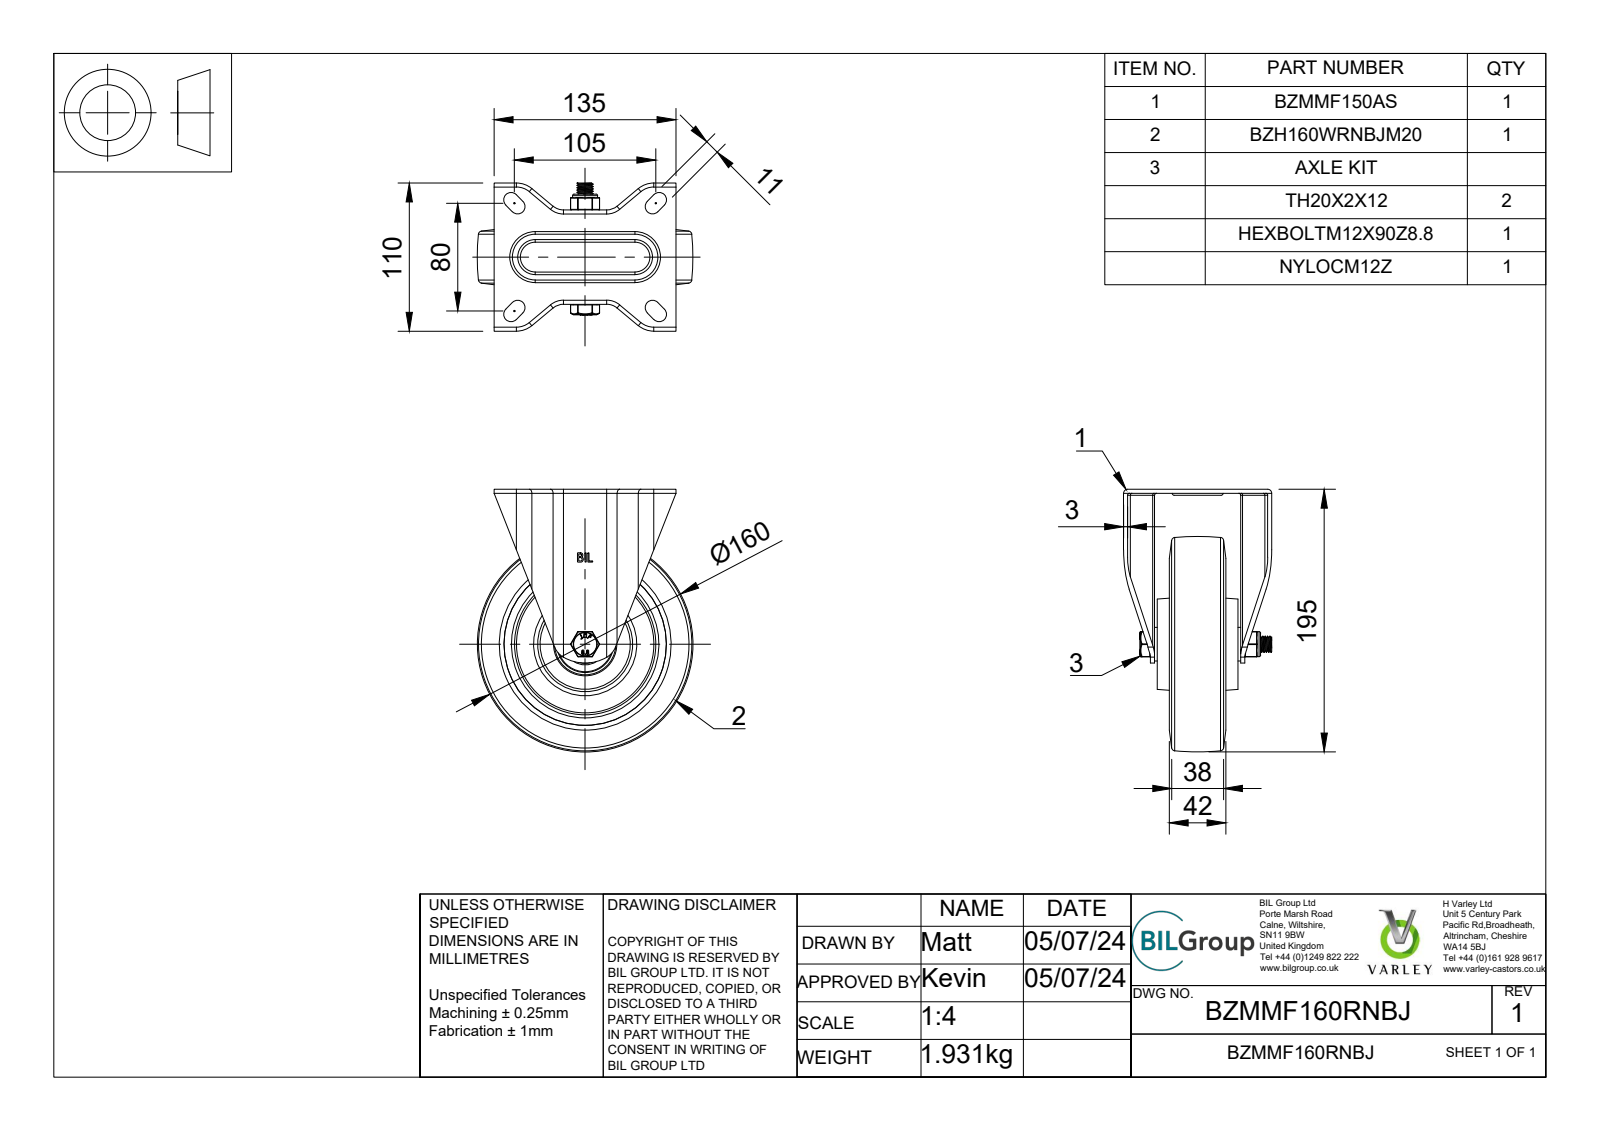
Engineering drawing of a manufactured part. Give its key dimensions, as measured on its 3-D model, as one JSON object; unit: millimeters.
{"part_name": "BZMMF160RNBJ v3; BZMMF150AS - 64 v1; ZINC PLATED, PRESSED STEEL BRACKET; BZH160WRNBJM20 v1 (+7 more)", "step_written_by": "Autodesk Translation Framework v13.14.0.145 (AUTOMOTIVE_DESIGN)", "units": "millimeters", "bodies": {"solids": 35, "faces": 1115, "planar": 435, "cylindrical": 232, "other": 448}, "overall_size": [195, 160, 110], "volume_mm3": 776155, "surface_area_mm2": 238124, "round_holes": [[12, 1], [12.2, 1], [12.25, 1], [14, 1], [20, 1], [28.5, 1], [30.8, 1], [40.3, 1], [40.5, 1], [42, 1], [47, 1], [120.5, 1]], "round_bosses_or_shafts": [[40.8, 1], [31.3, 1], [27, 1], [25, 1], [24, 1], [19.8, 1], [18.5, 1], [17.75, 1]], "partial_cylinders_radius": [[0.5, 20], [1.5, 12], [3, 8], [5.5, 8], [0.47, 4], [0.9, 4], [2, 4], [6, 4]], "face_to_face_distances": [3, 31, 36, 39, 14, 17, 56, 51, 25, 67]}
